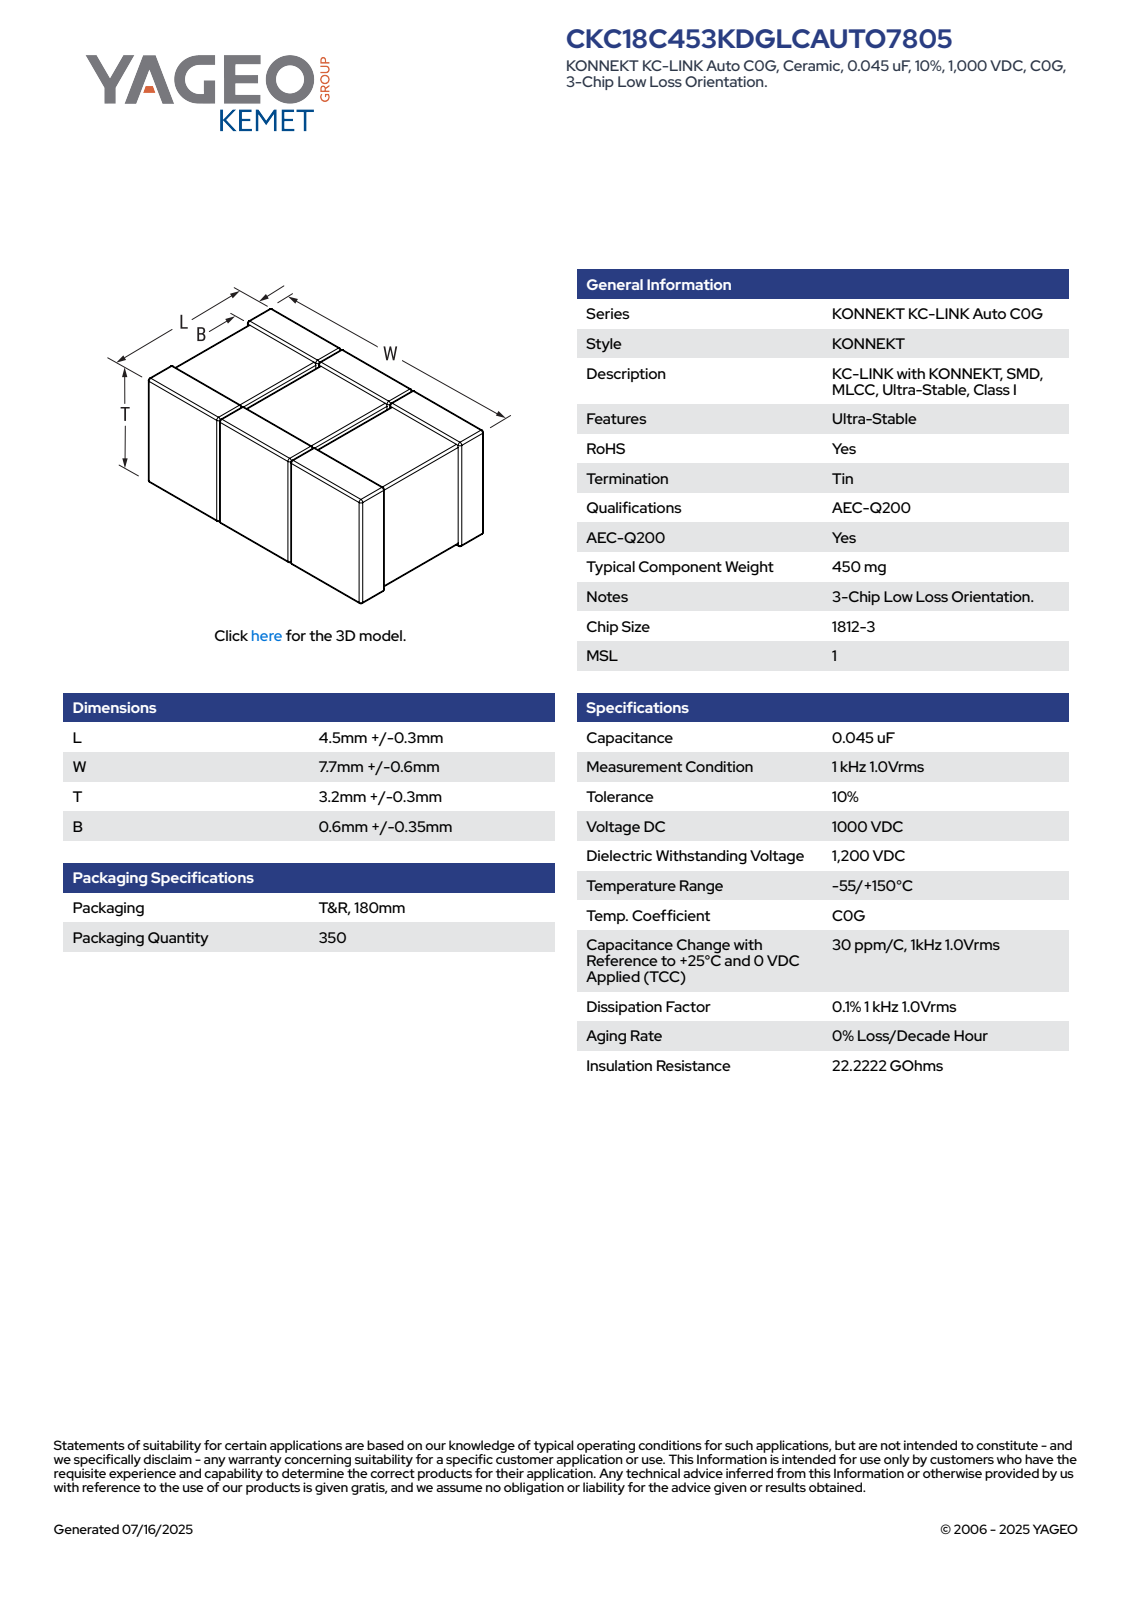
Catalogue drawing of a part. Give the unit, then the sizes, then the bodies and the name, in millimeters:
Units: millimetres
Overall size (bounding box): 8.3 × 4.8 × 3.5
Main face-to-face distances: 2.7, 2.77, 5.46, 5.53, 2.76, 4.8, 3.43, 3.36, 2.83, 2.69
Volume: 132 mm³ · Surface area: 236 mm²
Bodies: 12 solids, 351 faces (213 planar, 90 cylindrical, 48 other)
Part name (STEP PRODUCT): CCSS_K3LL_1812-3_L4.8W8.3B0.95T3.5
STEP written by: SolidWorks 2021 (AUTOMOTIVE_DESIGN)
